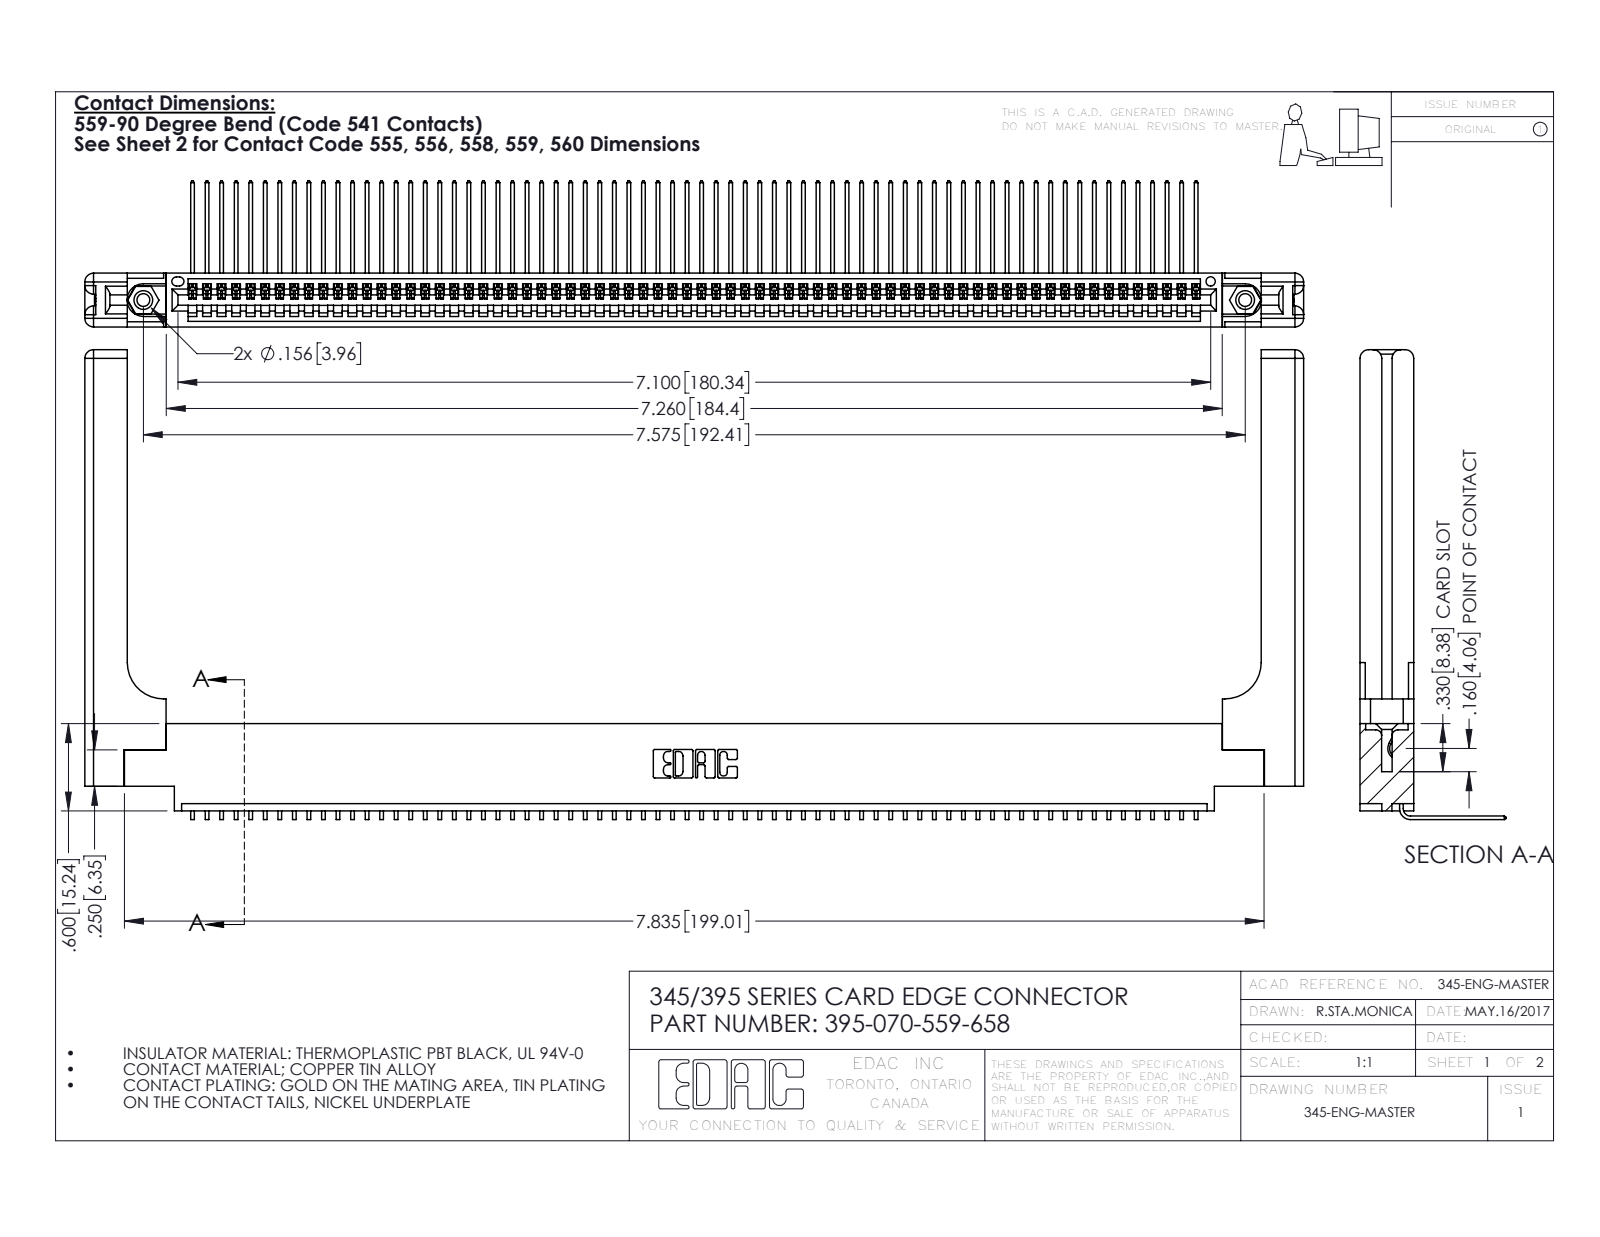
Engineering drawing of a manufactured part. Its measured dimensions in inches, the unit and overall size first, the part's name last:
Units: inches
Overall size (bounding box): 8.379 × 3.229 × 1.005
Round holes (diameter × count): ⌀0.089 ×2, ⌀0.125 ×2, ⌀0.156 ×2, ⌀0.064 ×1
Round bosses / shafts (diameter × count): ⌀0.155 ×2
Partial cylindrical surfaces — rounded edges, fillets, slot ends (radius × count): R0.006 ×140, R0.01 ×22, R0.06 ×16, R0.007 ×6, R0.031 ×6, R0.026 ×3, R0.03 ×2, R0.031 ×2
Main face-to-face distances: 0.072, 0.37, 0.298, 0.098, 0.272, 0.025, 0.2, 0.225, 0.148, 0.15
Hole centre spacings: 0.27, 7.339, 7.575
Volume: 1.774 in³ · Surface area: 53.49 in²
Bodies: 75 solids, 4586 faces (3172 planar, 1354 cylindrical, 60 other)
Part name (STEP PRODUCT): 345-220-058_345-220-058; 345-292-001_558 559 Tail - 1; 345-250-001_345-250-001-102; 395-070-559-658 (+1 more)
STEP written by: SolidWorks 2016 (CONFIG_CONTROL_DESIGN)
